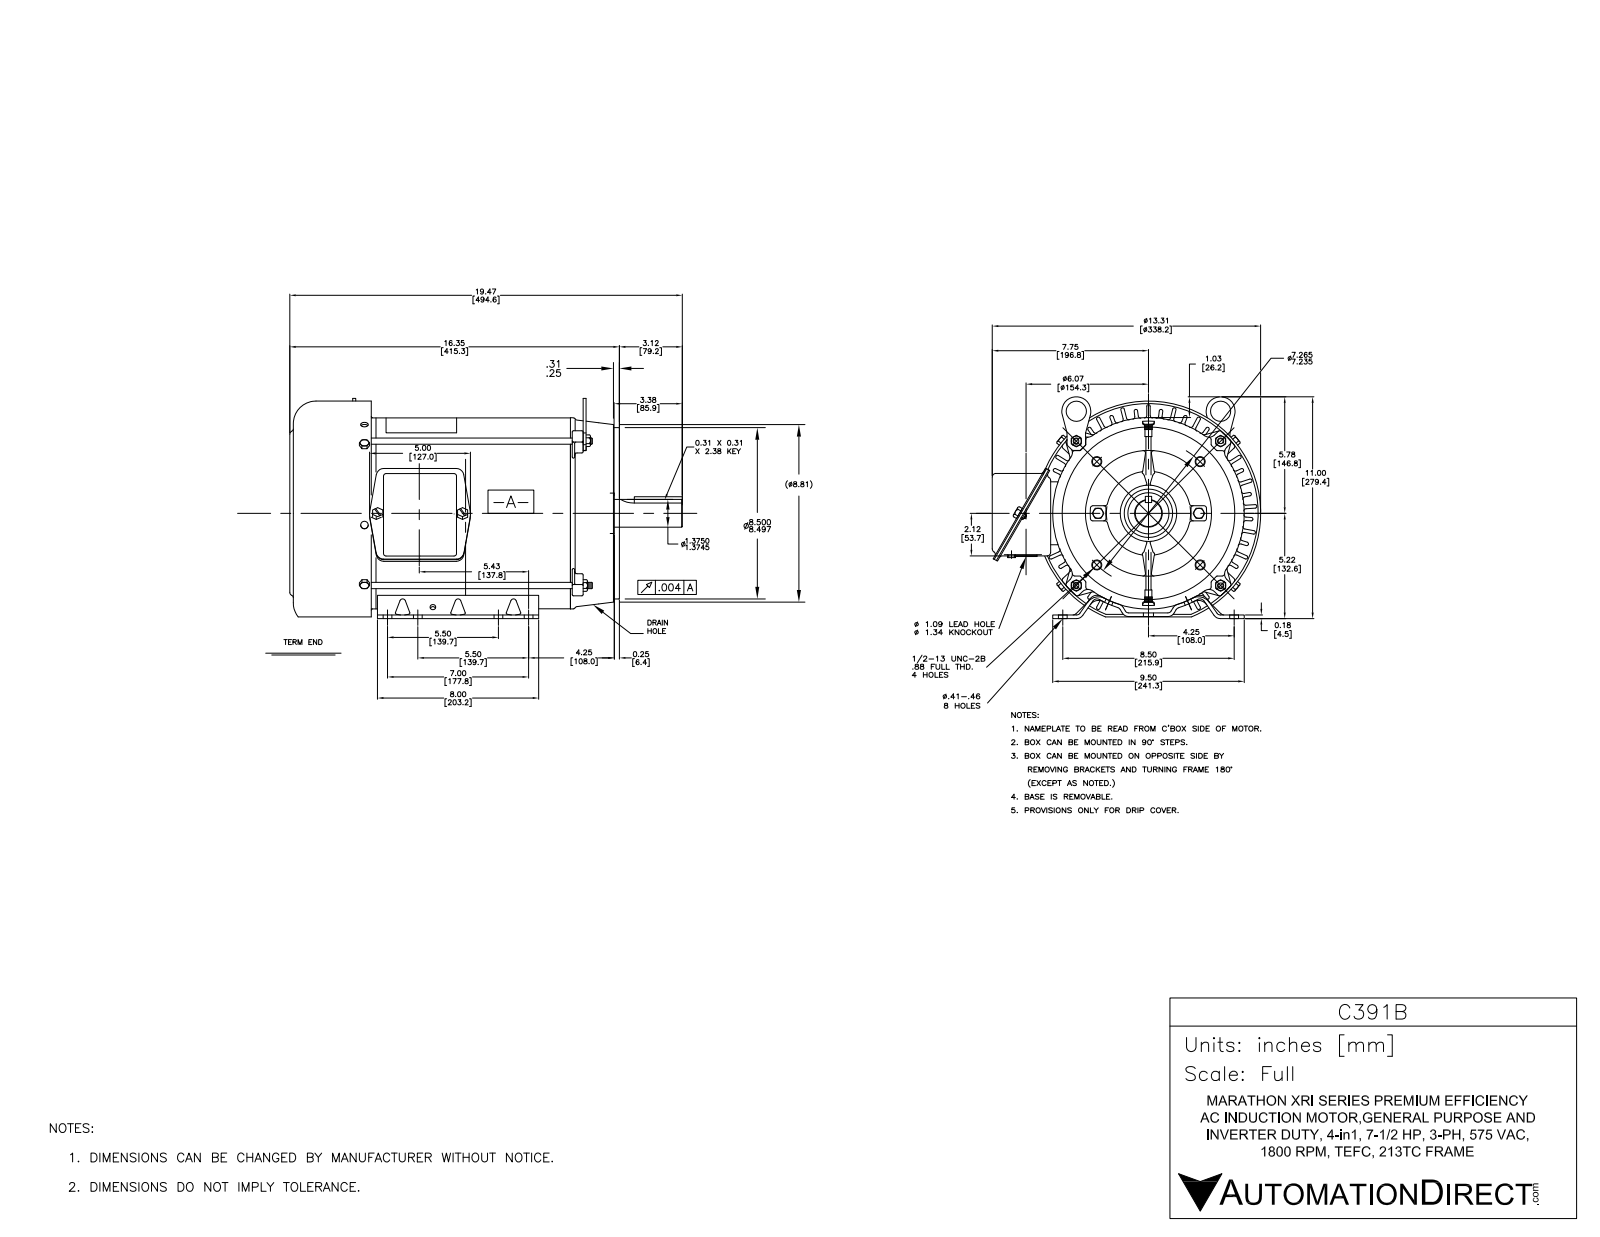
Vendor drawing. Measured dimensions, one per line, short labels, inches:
name: C389B 1st
written by: SolidWorks 2017 (AUTOMOTIVE_DESIGN)
unit: in
bodies: 38 solids, 3568 faces (1121 planar, 1147 cylindrical, 1300 other)
size: 19.466 × 13.307 × 11.007
volume: 195.3 in³; area: 2 147 in²
holes: 10× ⌀0.373, 6× ⌀0.278, 4× ⌀0.257, 4× ⌀0.32, 4× ⌀0.37, 4× ⌀0.422, 4× ⌀0.435, 4× ⌀0.435, 3× ⌀0.219, 3× ⌀0.267, 2× ⌀0.176, 2× ⌀0.218
bosses: 6× ⌀0.65, 6× ⌀0.324, 6× ⌀0.31, 6× ⌀0.25, 4× ⌀0.522, 2× ⌀1.16, 2× ⌀0.79, 2× ⌀0.44
rounds: 149× R0.13, 142× R0.06, 90× R0.12, 34× R0.25, 12× R0.03, 10× R0.18, 8× R0.04, 8× R0.14
face distances: 0.06, 0.17, 16.175, 0.12, 0.179, 2.734, 0.1, 16.345, 0.2, 0.179
hole spacings: 3.5, 6.224, 2.5, 7, 7.156, 1, 1.435, 1.5
